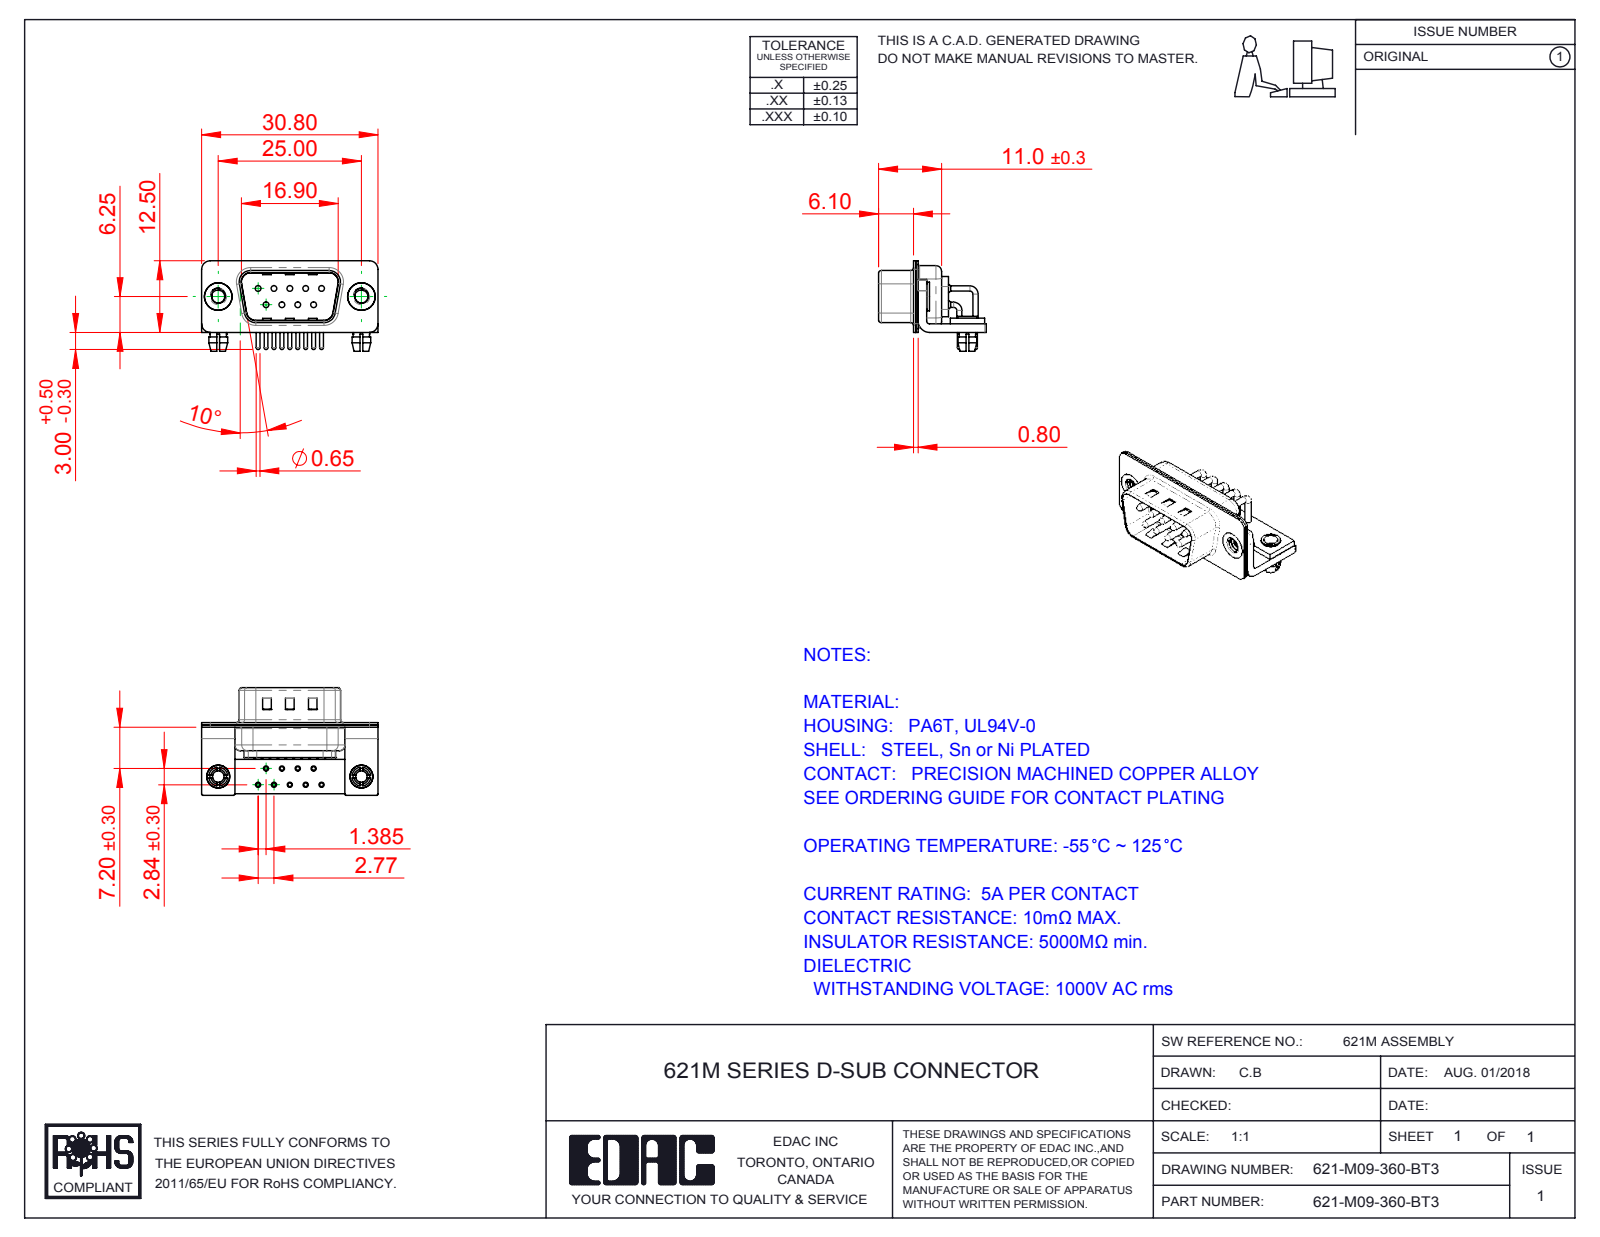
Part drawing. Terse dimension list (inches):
name: 621-M09-360-BT3; 621M Stabilizer Bracket; 621M Shell Rear_09 Contacts; 621M 4-40 Threaded Rivet_Stabilizer (+6 more)
written by: SolidWorks 2016 (CONFIG_CONTROL_DESIGN)
unit: in
bodies: 19 solids, 1454 faces (757 planar, 525 cylindrical, 172 other)
size: 1.213 × 0.74 × 0.622
volume: 0.11 in³; area: 7.835 in²
holes: 11× ⌀0.079, 9× ⌀0.035, 9× ⌀0.039, 9× ⌀0.067, 2× ⌀0.089, 2× ⌀0.098, 2× ⌀0.126, 2× ⌀0.157, 2× ⌀0.189
bosses: 9× ⌀0.059, 9× ⌀0.035, 9× ⌀0.026, 2× ⌀0.197, 2× ⌀0.193, 2× ⌀0.157, 2× ⌀0.134, 2× ⌀0.13
rounds: 16× R0.01, 16× R0.059, 13× R0.079, 9× R0.02, 9× R0.04, 8× R0.063, 4× R0.024, 4× R0.026
face distances: 0.016, 0.059, 0.031, 0.033, 0.049, 0.039, 0.409, 0.376, 0.098, 0.075
hole spacings: 0.124, 0.109, 0.218, 0.198, 0.198, 0.327, 0.294, 0.295
